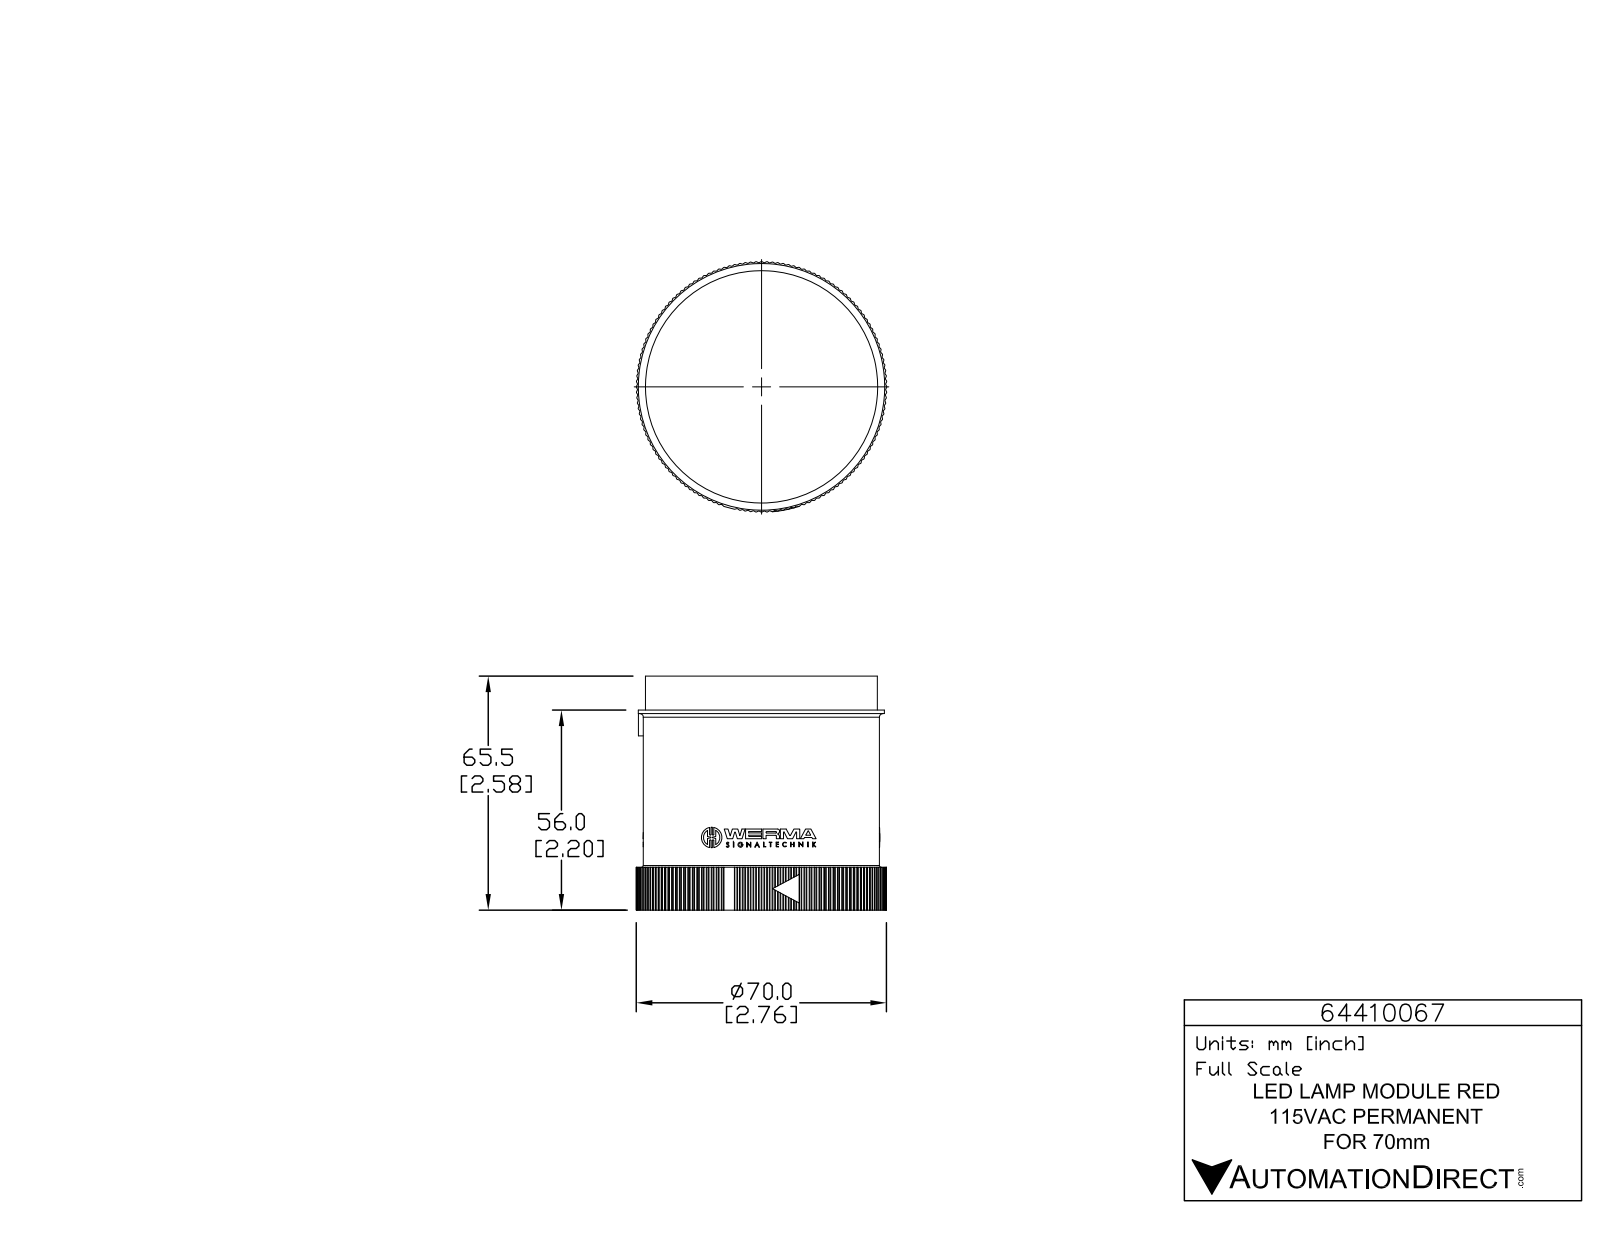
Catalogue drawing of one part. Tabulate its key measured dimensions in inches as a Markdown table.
| quantity | value |
| --- | --- |
| part name | 64410067 |
| STEP written by | SolidWorks 2015 (AUTOMOTIVE_DESIGN) |
| units | inches |
| bodies | 1 solid, 1400 faces (832 planar, 563 cylindrical, 5 other) |
| overall size | 2.762 × 2.762 × 2.579 |
| volume | 12.02 in³ |
| surface area | 37.48 in² |
| round holes (diameter × count) | 0.039 × 3, 2.575 × 1 |
| round bosses / shafts (diameter × count) | 0.226 × 3, 0.056 × 3, 2.717 × 1, 2.606 × 1, 2.559 × 1 |
| partial cylindrical surfaces (radius × count) | 0.008 × 285, 0.008 × 6, 0.008 × 6, 0.008 × 6, 0.131 × 6, 0.004 × 3, 0.005 × 3, 0.008 × 3 |
| main face-to-face distances | 2.201, 2.451, 0.378, 2.579, 2.205, 1.827, 0.374, 2.452, 0.472, 0.094 |
